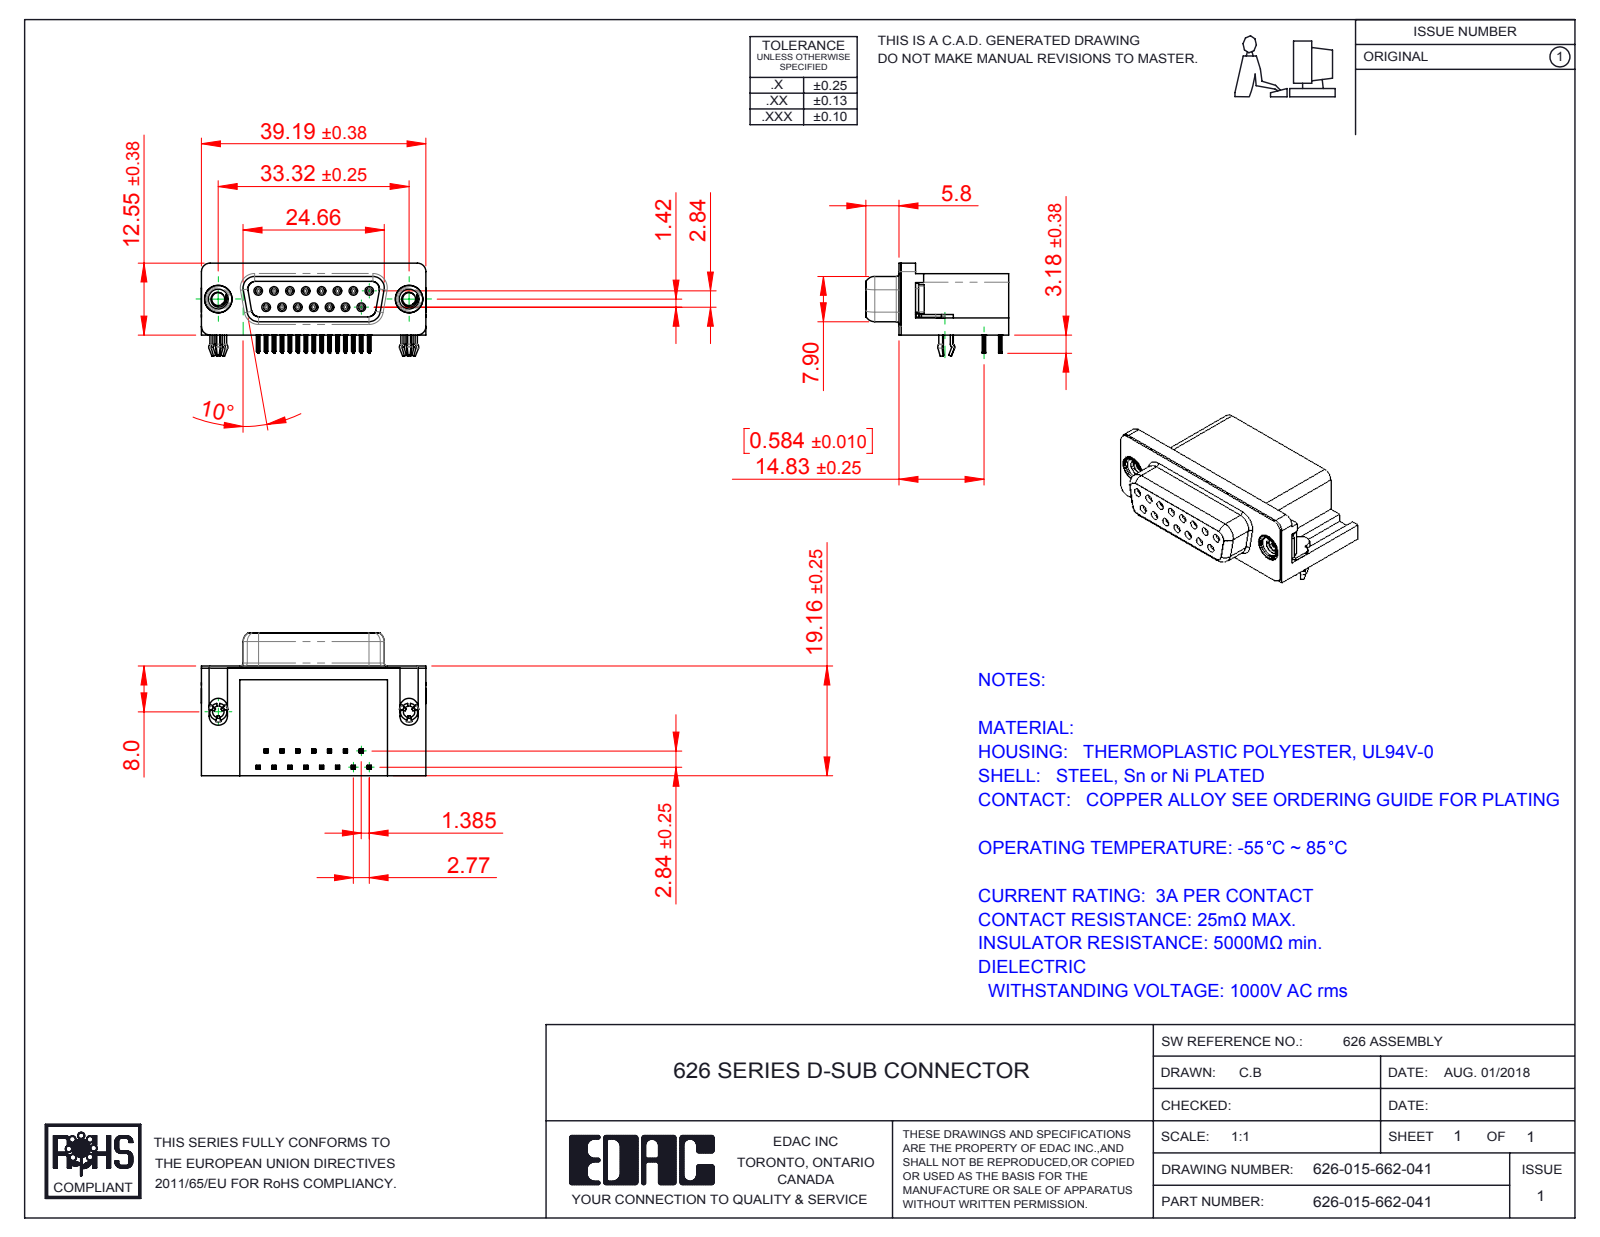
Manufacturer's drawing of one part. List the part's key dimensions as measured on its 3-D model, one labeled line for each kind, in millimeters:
Part name (STEP PRODUCT): 626 Contact Bottom; 626 3 Prong Board Lock; 626 Contact Top; 626-015-662-041 (+3 more)
STEP written by: SolidWorks 2016 (CONFIG_CONTROL_DESIGN)
Units: millimetres
Bodies: 21 solids, 2529 faces (1110 planar, 611 cylindrical, 808 other)
Overall size (bounding box): 39.22 × 24.96 × 16.25
Volume: 7 255 mm³ · Surface area: 8 091 mm²
Round holes (diameter × count): ⌀0.8 ×15, ⌀0.9 ×15, ⌀2 ×2, ⌀2.26 ×2, ⌀4 ×2, ⌀4.8 ×2, ⌀5 ×2
Round bosses / shafts (diameter × count): ⌀1.2 ×15, ⌀4.9 ×2, ⌀4.75 ×2, ⌀3.9 ×2, ⌀3 ×2
Partial cylindrical surfaces — rounded edges, fillets, slot ends (radius × count): R0.1 ×120, R0.15 ×60, R0.35 ×30, R1 ×18, R0.34 ×15, R0.25 ×12, R1.35 ×8, R1.6 ×8
Main face-to-face distances: 0.4, 10.35, 18.76, 0.35, 2.73, 6.2, 19.16, 10.7, 9.38, 3.18
Hole centre spacings: 3.16, 2.77, 5.54, 8.31, 11.08, 5.03, 5.04, 7.48
